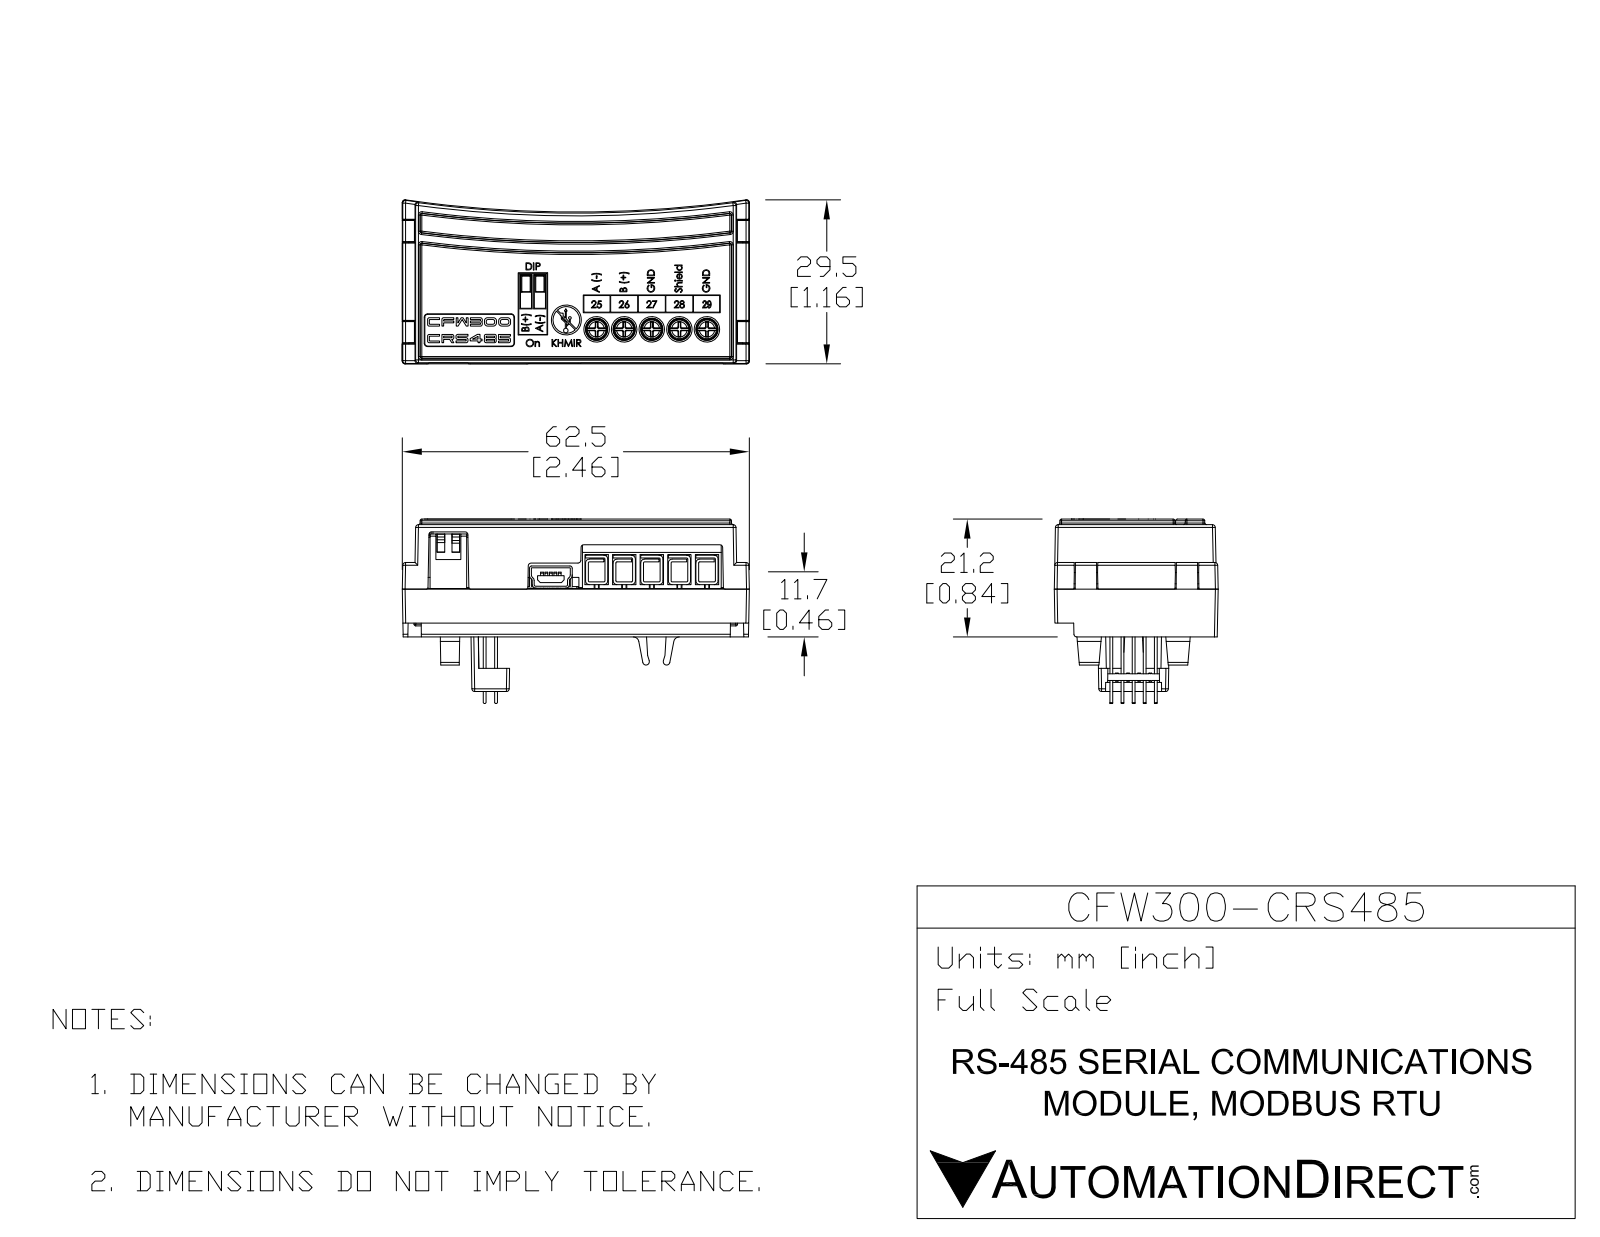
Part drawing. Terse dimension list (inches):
name: CFW300-CRS485
written by: SolidWorks 2017 (AUTOMOTIVE_DESIGN)
unit: in
bodies: 1 solid, 1067 faces (532 planar, 43 cylindrical, 492 other)
size: 2.461 × 1.159 × 0.845
volume: 2.164 in³; area: 11.5 in²
holes: 5× ⌀0.181, 1× ⌀0.191
bosses: 1× ⌀0.181
rounds: 11× R0.039, 6× R0.014, 4× R0.02, 4× R0.024, 1× R8.543
face distances: 0.835, 0.091, 2.37, 2.461, 0.098, 0.737, 2.28, 0.134, 0.528, 0.43
hole spacings: 0.196, 0.391, 0.587, 0.196, 0.386, 0.58, 0.775, 0.783
